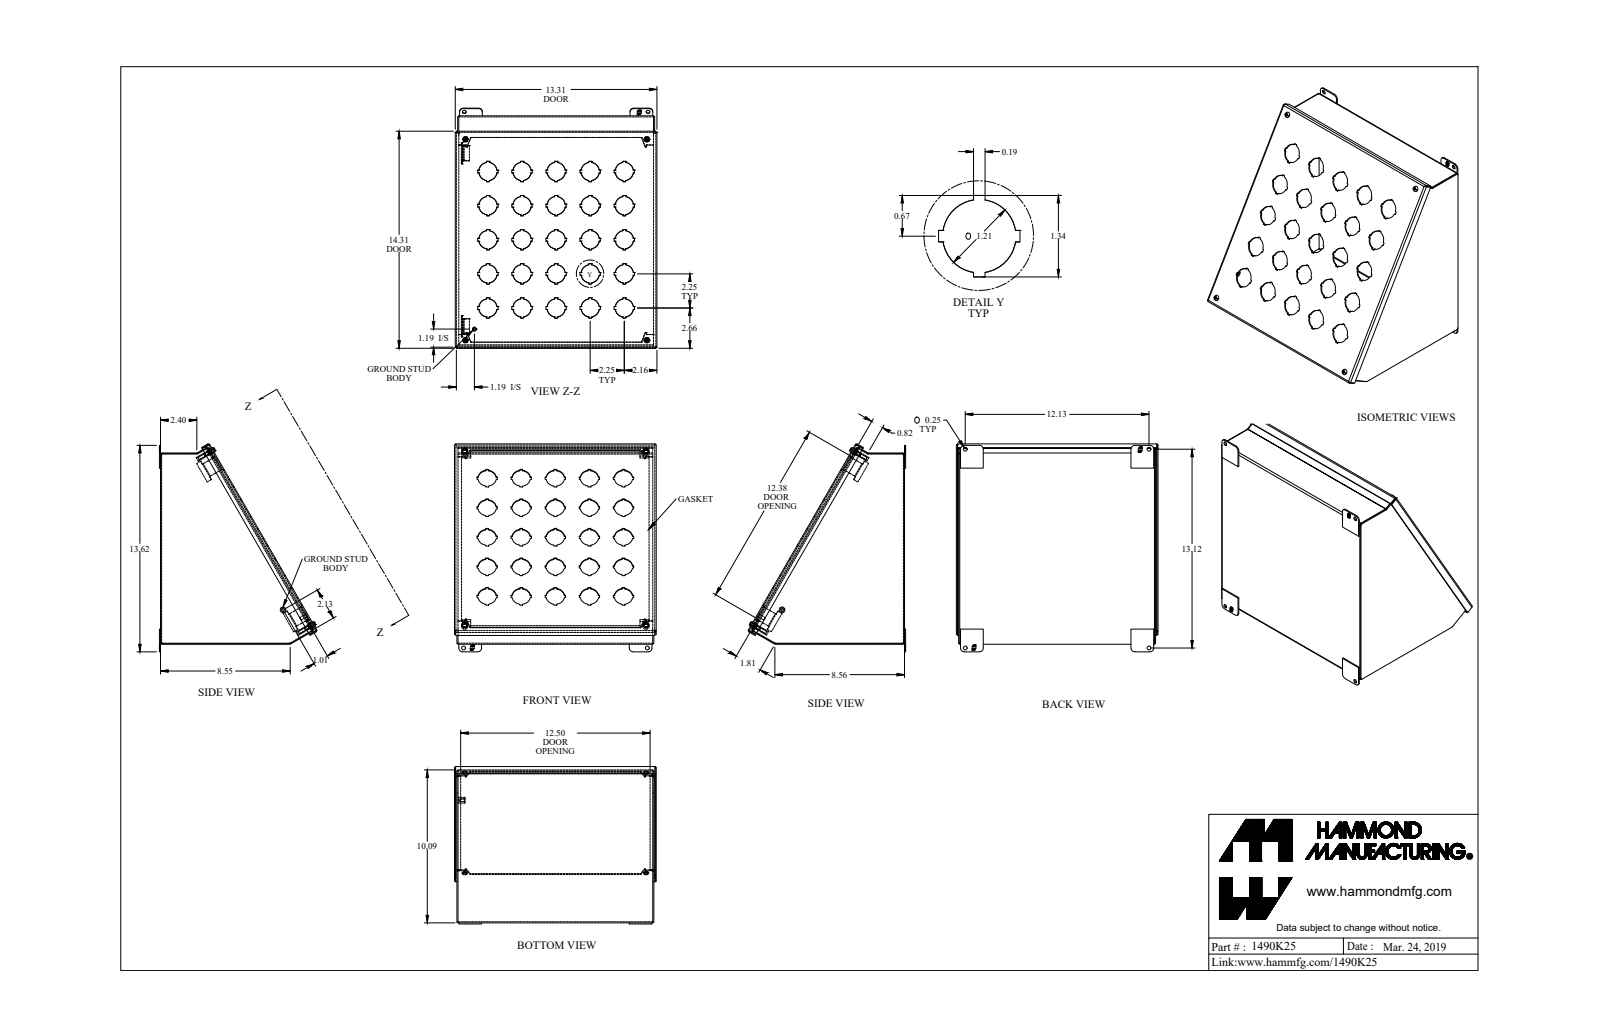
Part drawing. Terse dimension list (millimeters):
name: 1490K25_Default
written by: SolidWorks 2019 (CONFIG_CONTROL_DESIGN)
unit: mm
bodies: 25 solids, 1111 faces (799 planar, 272 cylindrical, 40 other)
size: 348.4 × 338.1 × 263.7
volume: 930 600 mm³; area: 990 300 mm²
holes: 25× ⌀30.7, 8× ⌀6.4, 4× ⌀4, 4× ⌀10.3, 1× ⌀4
bosses: 4× ⌀9.9, 4× ⌀7, 4× ⌀4.8, 4× ⌀3.8, 1× ⌀9.5, 1× ⌀6.4, 1× ⌀4.8
rounds: 18× R2.7, 12× R0.9, 8× R0.7, 8× R2.2, 8× R6.4, 4× R3.2, 4× R4.1, 4× R4.3
face distances: 1.8, 328.4, 1.8, 326.5, 330.2, 318.6, 320.4, 316.8, 6.4, 8.2
hole spacings: 127.8, 57.2, 80.8, 180.7, 114.3, 171.5, 206, 235.6
